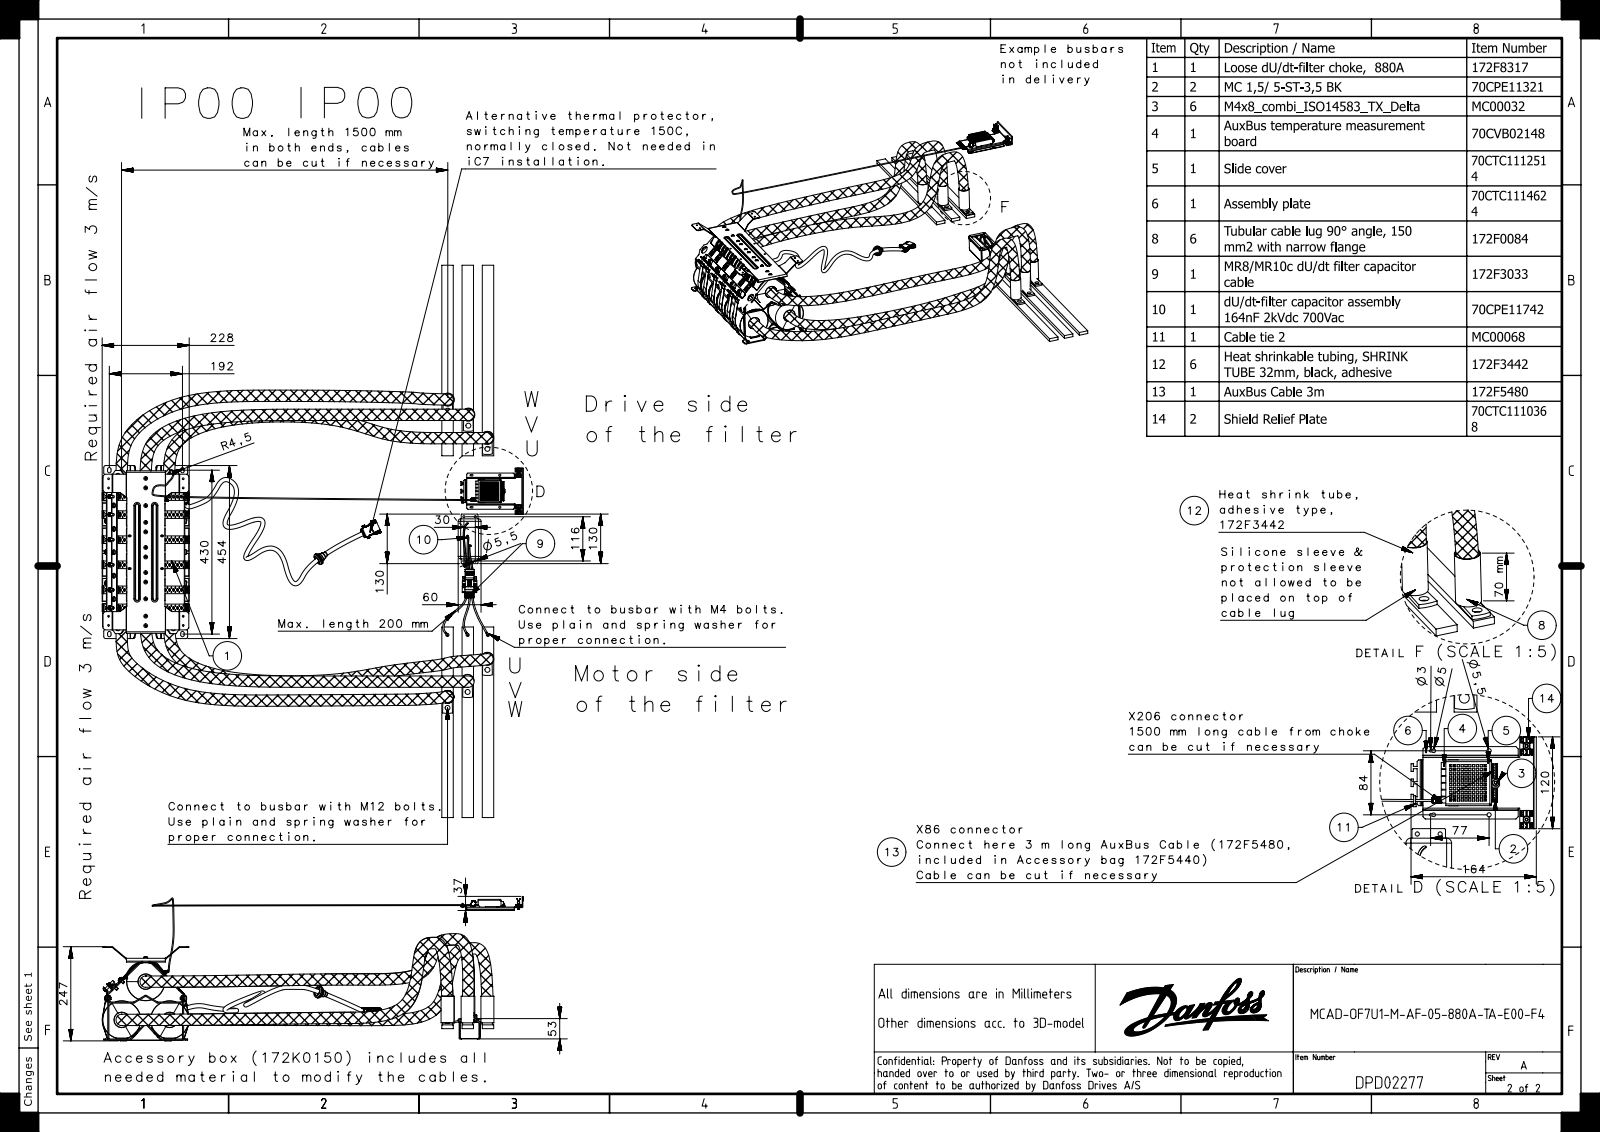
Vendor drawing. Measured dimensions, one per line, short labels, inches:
name: 70CPE11286; 70CMR00161; 70CPE07576; 70CPE05327 (+8 more)
written by: SIEMENS PLM Software NX 1892 (AUTOMOTIVE_DESIGN)
unit: in
bodies: 159 solids, 6744 faces (4778 planar, 1270 cylindrical, 696 other)
size: 43.484 × 34.01 × 15.411
volume: 924.5 in³; area: 4 546 in²
holes: 12× ⌀0.114, 12× ⌀0.177, 8× ⌀0.063, 8× ⌀0.157, 6× ⌀0.217, 6× ⌀0.512, 6× ⌀0.736, 6× ⌀1.654, 4× ⌀0.13, 4× ⌀0.984, 3× ⌀0.071, 3× ⌀0.165
bosses: 15× ⌀0.039, 12× ⌀1.339, 12× ⌀0.394, 10× ⌀0.11, 6× ⌀2.362, 6× ⌀2.283, 6× ⌀1.976, 6× ⌀0.945
rounds: 92× R0.004, 61× R0.02, 59× R0.01, 52× R0.008, 43× R0.039, 40× R0.016, 35× R0.03, 31× R0.118
face distances: 0.118, 2.598, 5.197, 2.362, 0.039, 0.236, 7.795, 4.961, 0.079, 7.559
hole spacings: 0.138, 0.276, 0.2, 0.014, 0.413, 0.945, 1.142, 1.28
